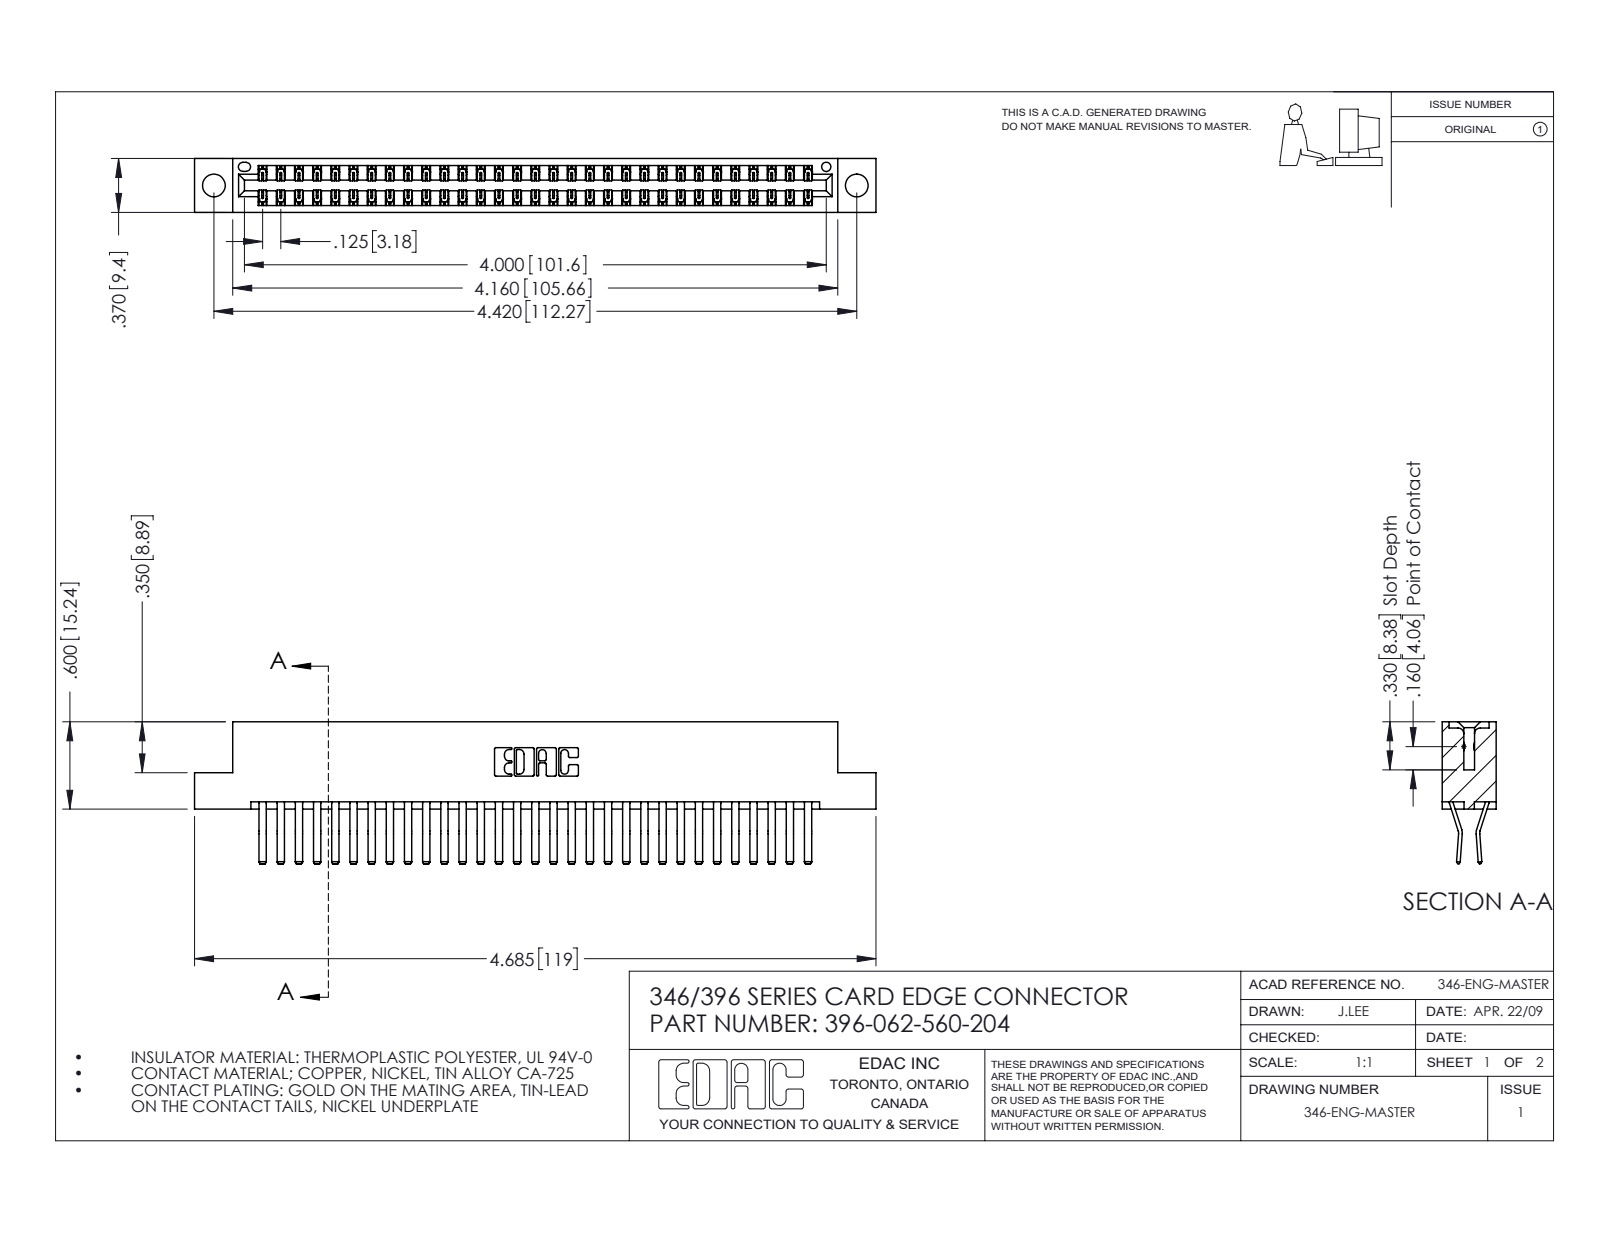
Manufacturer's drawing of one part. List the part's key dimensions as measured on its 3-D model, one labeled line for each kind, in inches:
Part name (STEP PRODUCT): 345-292-001_560 Tail; 346 Part_Flush Mounting Lugs - 0.156 Dia-TH; 396-062-560-204
STEP written by: SolidWorks 2016 (CONFIG_CONTROL_DESIGN)
Units: inches
Bodies: 63 solids, 3470 faces (2246 planar, 1224 cylindrical, 0 other)
Overall size (bounding box): 4.685 × 0.975 × 0.37
Volume: 0.722 in³ · Surface area: 26.34 in²
Round holes (diameter × count): ⌀0.156 ×2, ⌀0.064 ×1
Partial cylindrical surfaces — rounded edges, fillets, slot ends (radius × count): R0.006 ×93, R0.01 ×22, R0.007 ×6, R0.031 ×6, R0.026 ×3, R0.01 ×2, R0.014 ×2, R0.022 ×2
Main face-to-face distances: 0.048, 0.322, 0.37, 0.25, 0.025, 0.072, 0.298, 0.275, 0.148, 0.222
Hole centre spacings: 0.246, 4.212, 4.42
